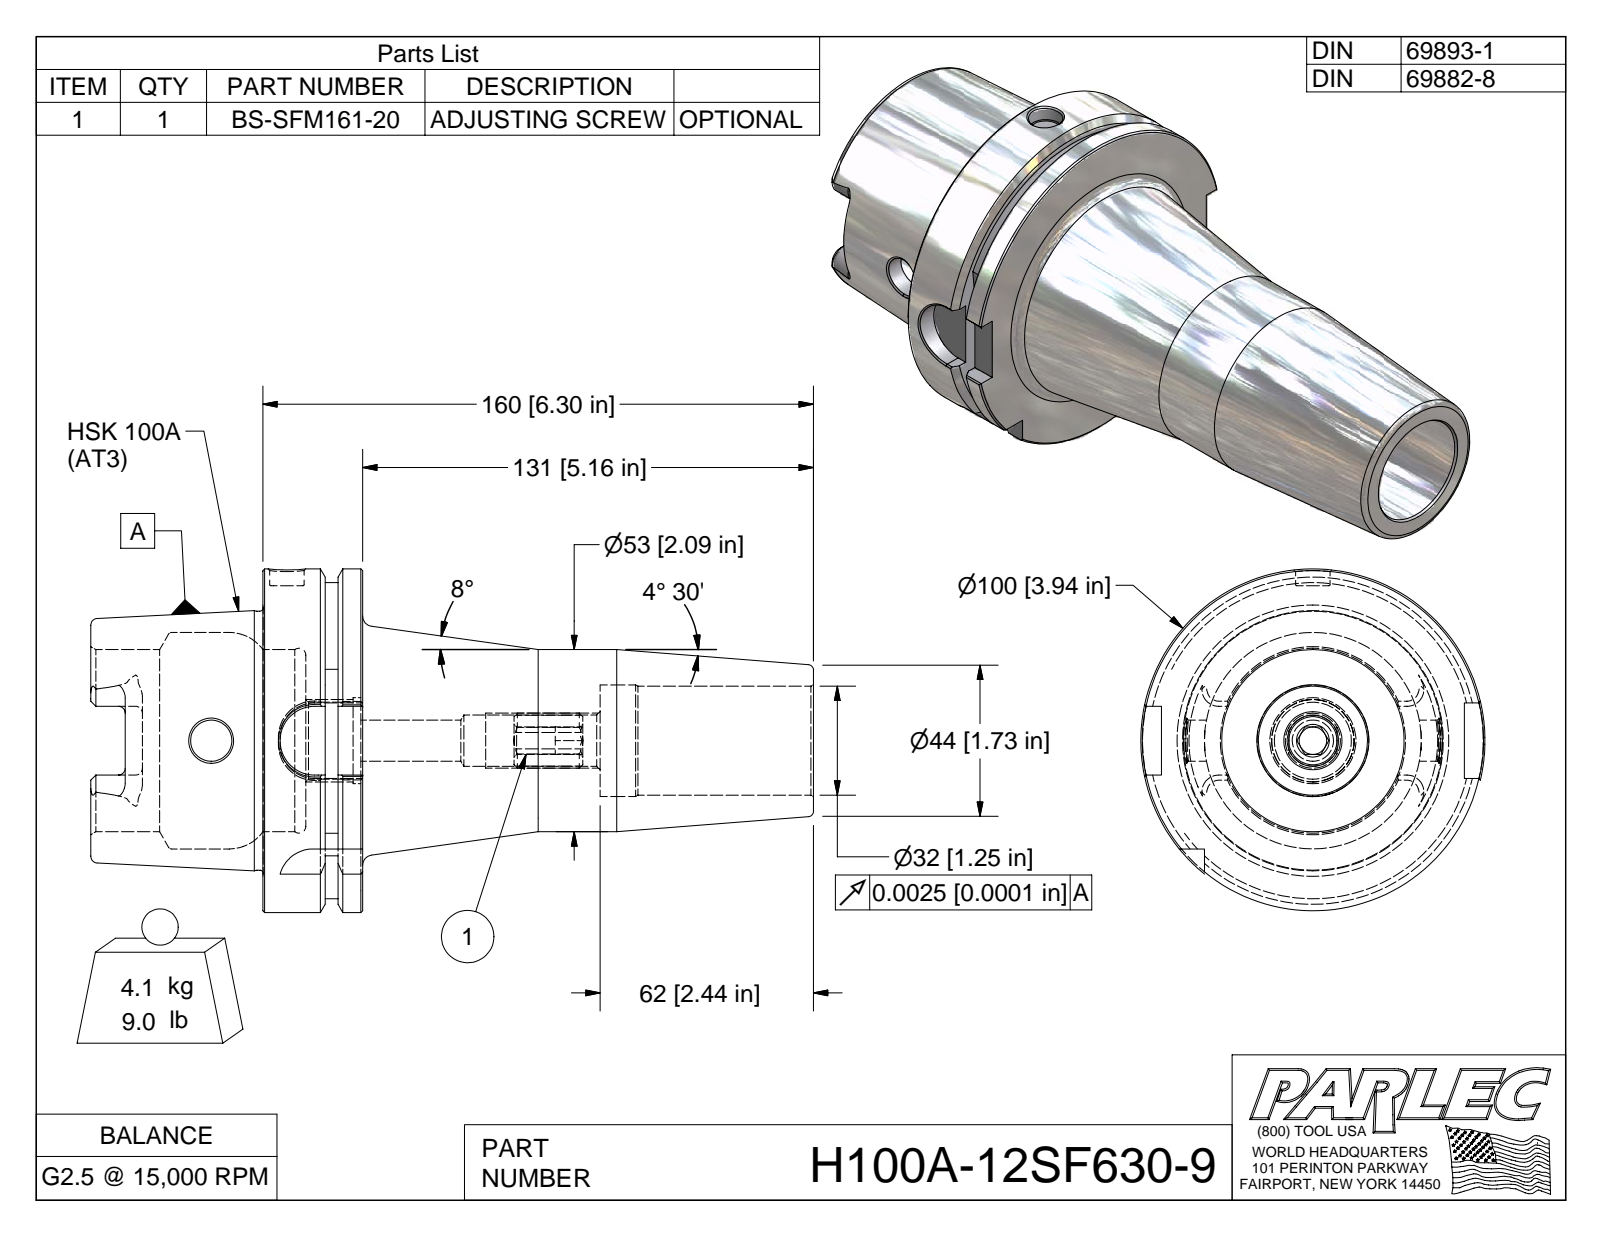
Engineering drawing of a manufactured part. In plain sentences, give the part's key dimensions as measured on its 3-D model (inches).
The part is named "H100A-12SF630-9; H100A-12SF630-9-1; BS-SFM161-20". Its 3-D file was written by "Autodesk Inventor 2009 (AUTOMOTIVE_DESIGN)". It is 2 solids with 150 faces: 49 planar, 30 cylindrical and 71 other. Overall it measures 8.269 by 3.937 by 3.937 inches. Its volume is 30.46 cubic inches and its surface area 125.1 square inches. Round holes: 1 of diameter 0.394, 1 of diameter 0.472, 1 of diameter 0.881, 1 of diameter 0.985, 1 of diameter 1.248, 1 of diameter 1.278, 1 of diameter 2.087, 1 of diameter 2.48. Round bosses or shafts: 1 of diameter 3.937, 1 of diameter 2.967. Partial cylindrical surfaces (rounded edges, fillets, slot ends): 4 of radius 0.394, 3 of radius 0.079, 2 of radius 0.192, 1 of radius 0.315, 1 of radius 1.811. The main face-to-face distances are 1.142, 0.492, 0.65, 1.969, 2.461, 3.11, 5.828, 3.859, 3.367, 2.717.
